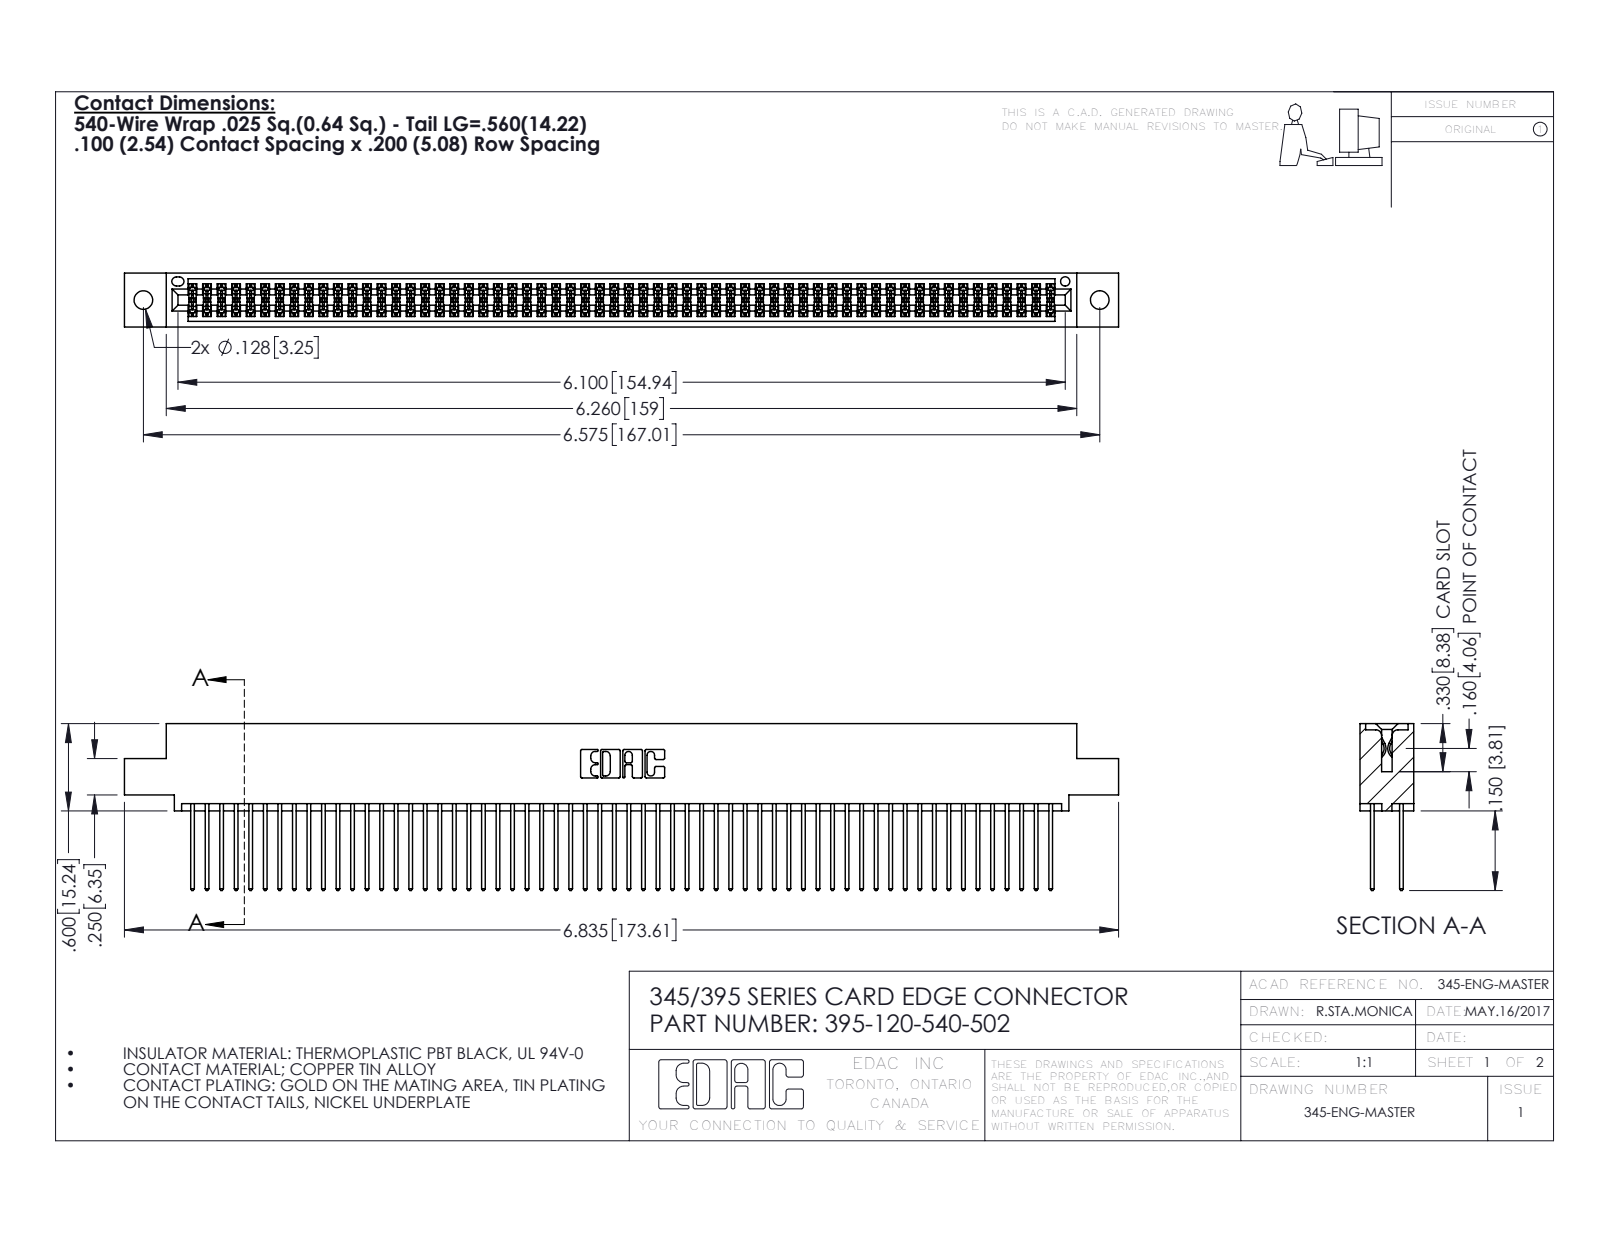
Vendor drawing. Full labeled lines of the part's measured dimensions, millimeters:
Part name (STEP PRODUCT): 345-292-001_345-293-140; 345 Part_0.110 Offset - 0.128 Dia; 395-120-540-502
STEP written by: SolidWorks 2016 (CONFIG_CONTROL_DESIGN)
Units: millimetres
Bodies: 121 solids, 6130 faces (4044 planar, 2086 cylindrical, 0 other)
Overall size (bounding box): 173.6 × 29.1 × 9.4
Volume: 17 370 mm³ · Surface area: 27 970 mm²
Round holes (diameter × count): ⌀3.3 ×2, ⌀1.6 ×1
Partial cylindrical surfaces — rounded edges, fillets, slot ends (radius × count): R0.2 ×180, R0.3 ×120, R0.3 ×22, R0.2 ×6, R0.8 ×6, R0.7 ×3, R0.4 ×2, R0.5 ×2
Main face-to-face distances: 1.8, 7.6, 5.1, 2.5, 6.9, 0.6, 9.4, 5.7, 4.4, 3.8
Hole centre spacings: 6.9, 161, 167
